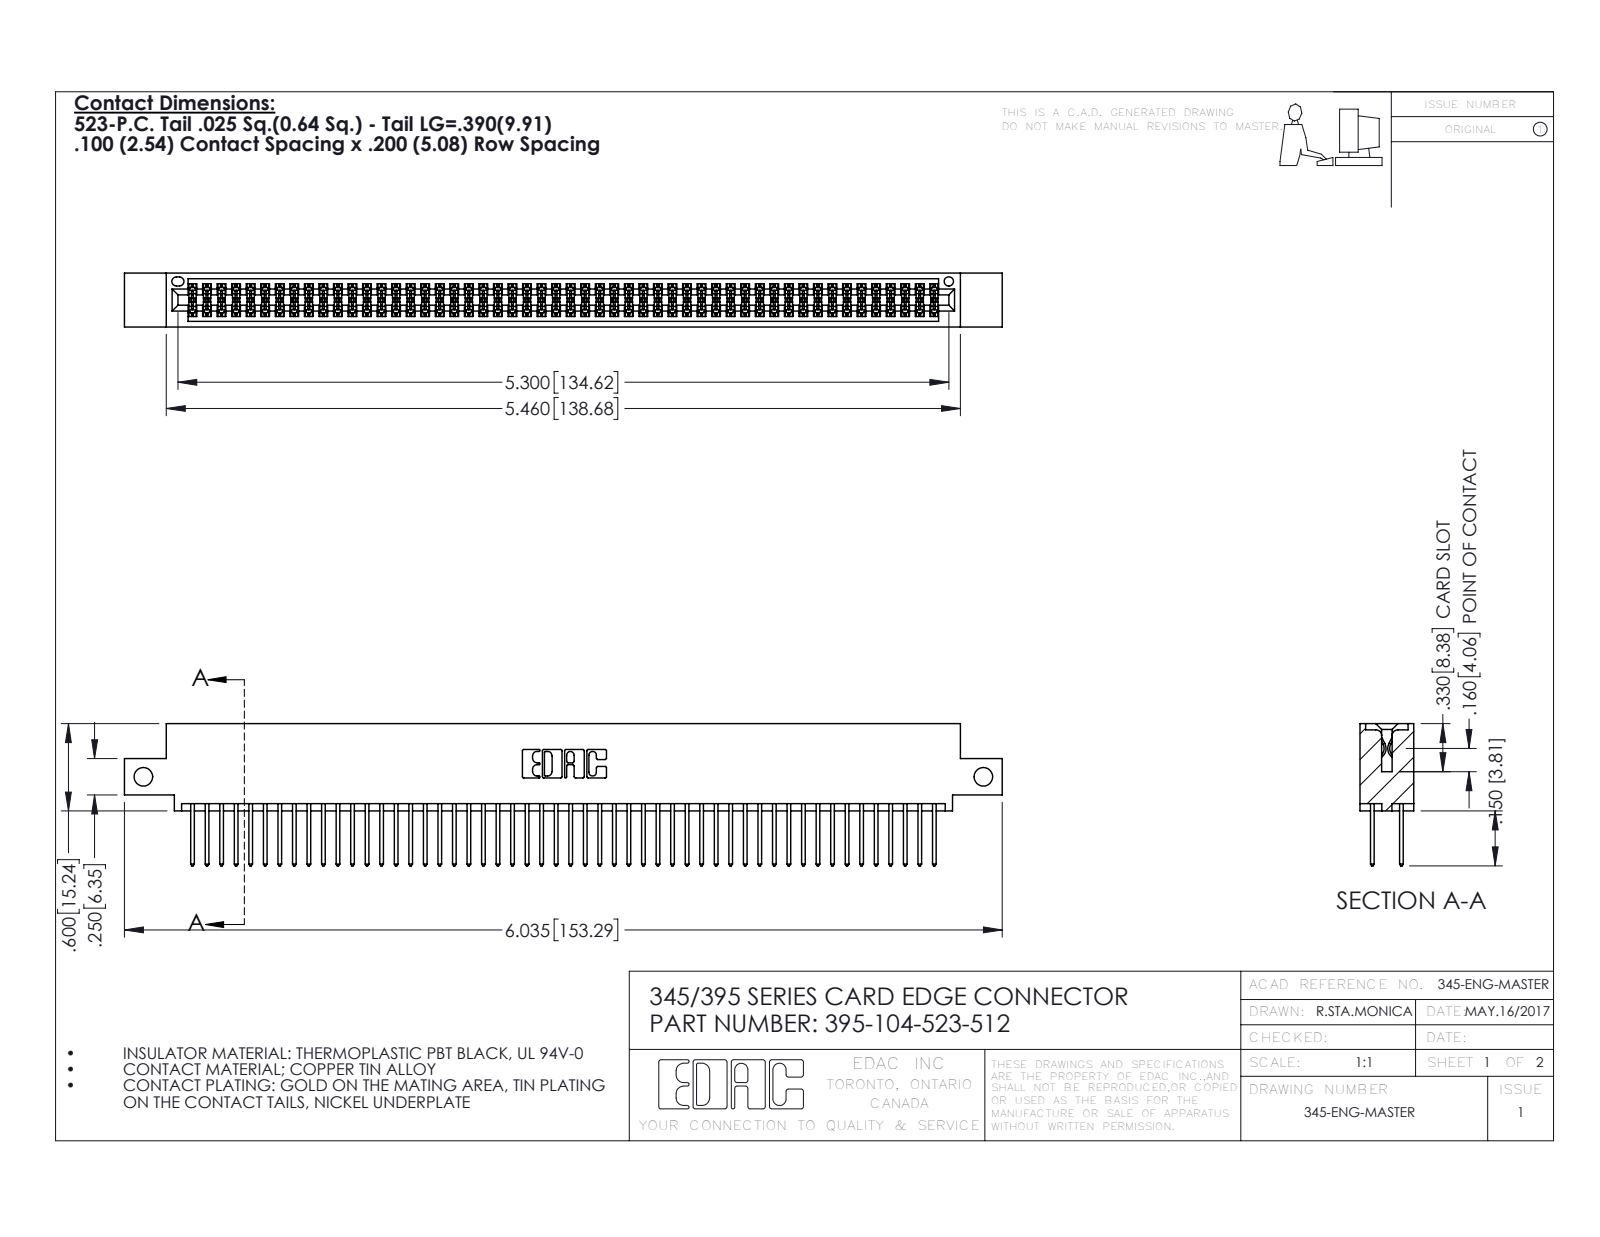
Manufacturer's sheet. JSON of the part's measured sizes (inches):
{"part_name": "345 Part_0.110 Offset - Side Mount; 345-292-001_345-293-123; 395-104-523-512", "step_written_by": "SolidWorks 2016 (CONFIG_CONTROL_DESIGN)", "units": "inches", "bodies": {"solids": 105, "faces": 5330, "planar": 3516, "cylindrical": 1814, "other": 0}, "overall_size": [6.035, 0.977, 0.37], "volume_in3": 0.918, "surface_area_in2": 36.17, "round_holes": [[0.128, 2], [0.064, 1]], "partial_cylinders_radius": [[0.006, 156], [0.01, 104], [0.01, 22], [0.007, 6], [0.031, 6], [0.026, 3], [0.014, 2], [0.019, 2]], "face_to_face_distances": [0.298, 0.072, 0.2, 0.098, 0.272, 0.025, 0.37, 0.225, 0.175, 0.149], "hole_center_spacings": [5.775]}
